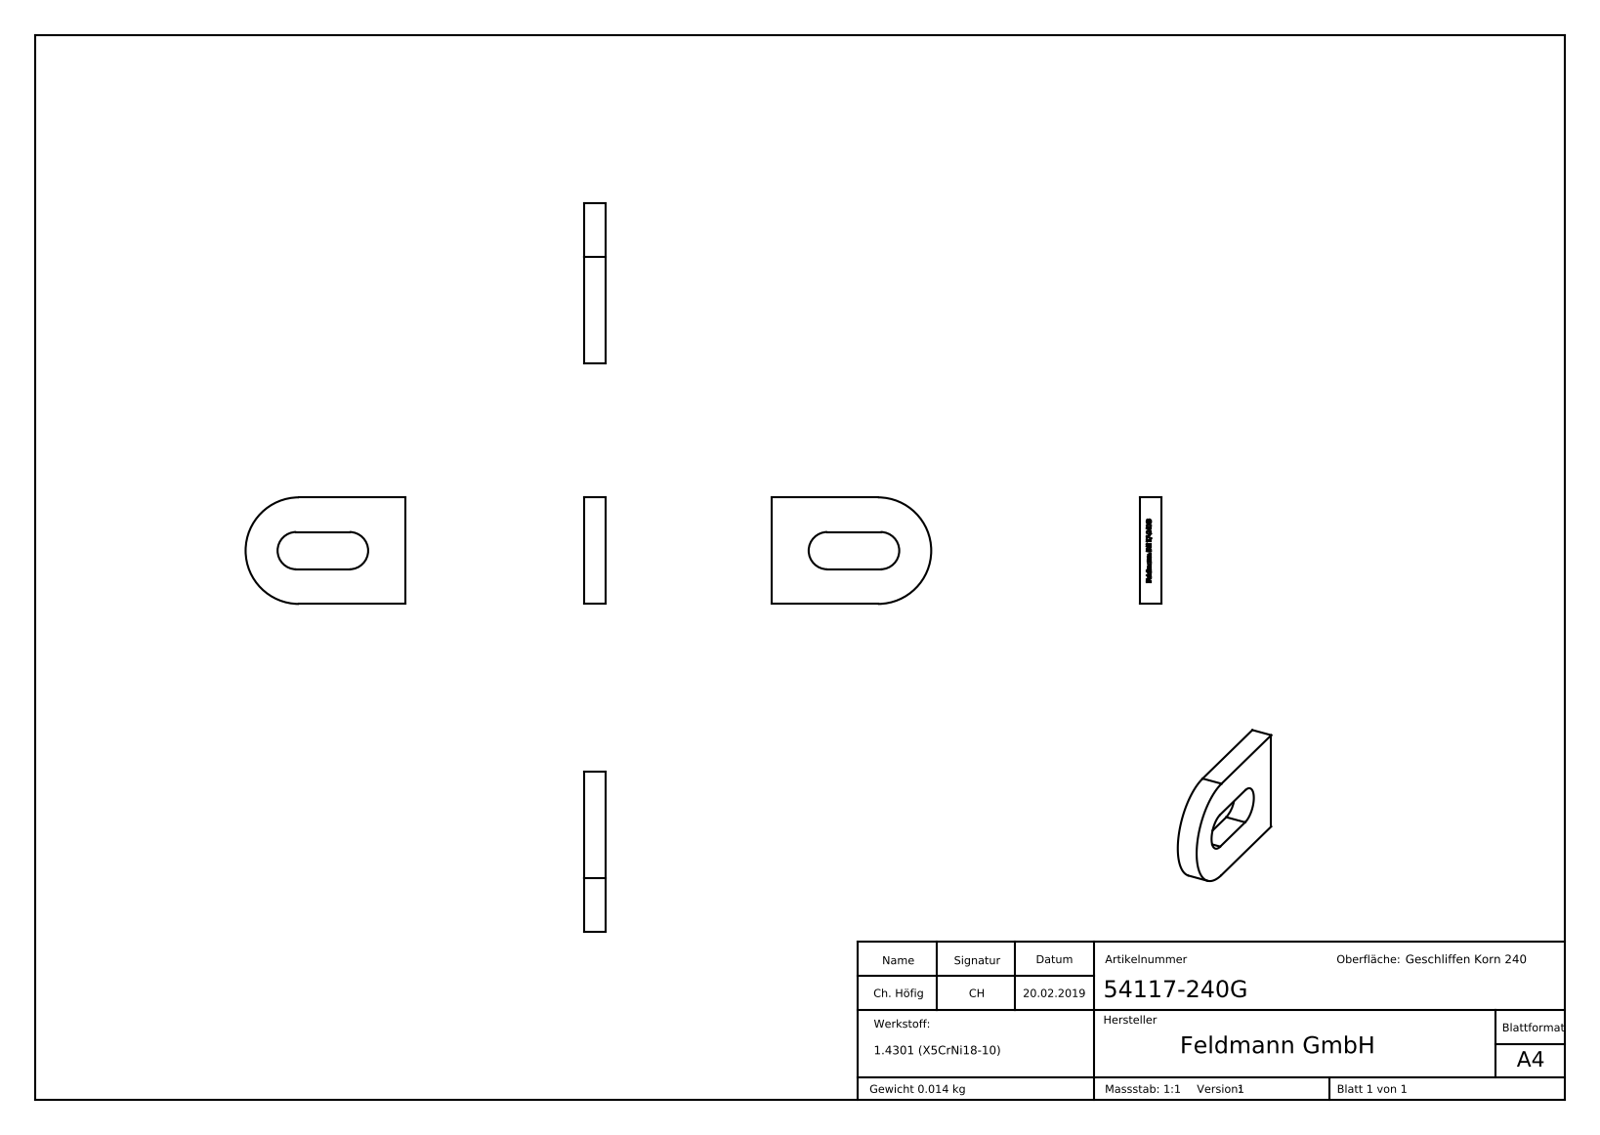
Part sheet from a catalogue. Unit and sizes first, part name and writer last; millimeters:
Units: millimetres
Overall size (bounding box): 30 × 20 × 4
Partial cylindrical surfaces — rounded edges, fillets, slot ends (radius × count): R3.5 ×2, R10 ×1
Main face-to-face distances: 4, 6.5, 13.5, 20, 7, 2, 0.61, 1.21, 0.53, 1.29
Volume: 1 794 mm³ · Surface area: 1 437 mm²
Bodies: 1 solid, 234 faces (149 planar, 5 cylindrical, 80 other)
Part name (STEP PRODUCT): 54117-240G
STEP written by: SolidWorks 2015 (CONFIG_CONTROL_DESIGN)
